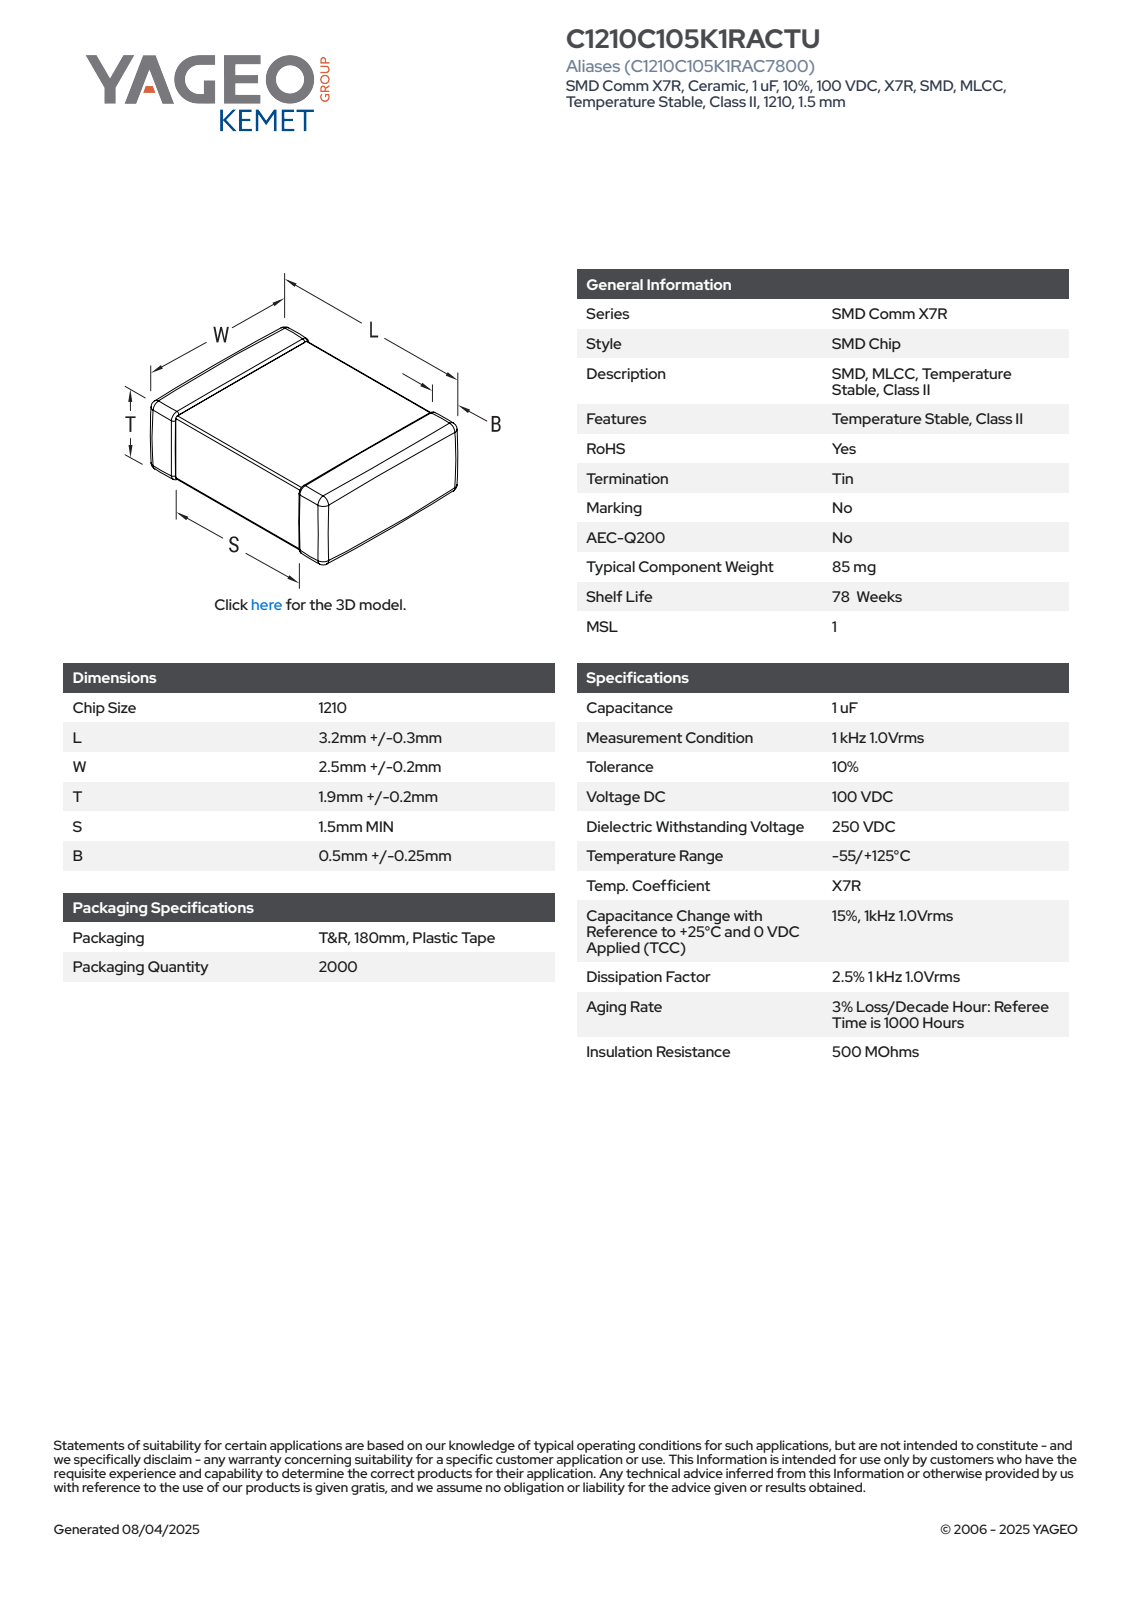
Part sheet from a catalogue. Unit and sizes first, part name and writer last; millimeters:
Units: millimetres
Overall size (bounding box): 3.5 × 2.7 × 2.1
Main face-to-face distances: 2.04, 3.5, 2.64, 1.98, 2.58, 2.1, 2.7, 2.05, 1.99, 0.4
Volume: 19 mm³ · Surface area: 45 mm²
Bodies: 4 solids, 125 faces (71 planar, 38 cylindrical, 16 other)
Part name (STEP PRODUCT): CCS_CCSTD_1210_L3.5W2.7T2.1B0.5
STEP written by: SolidWorks 2021 (AUTOMOTIVE_DESIGN)
